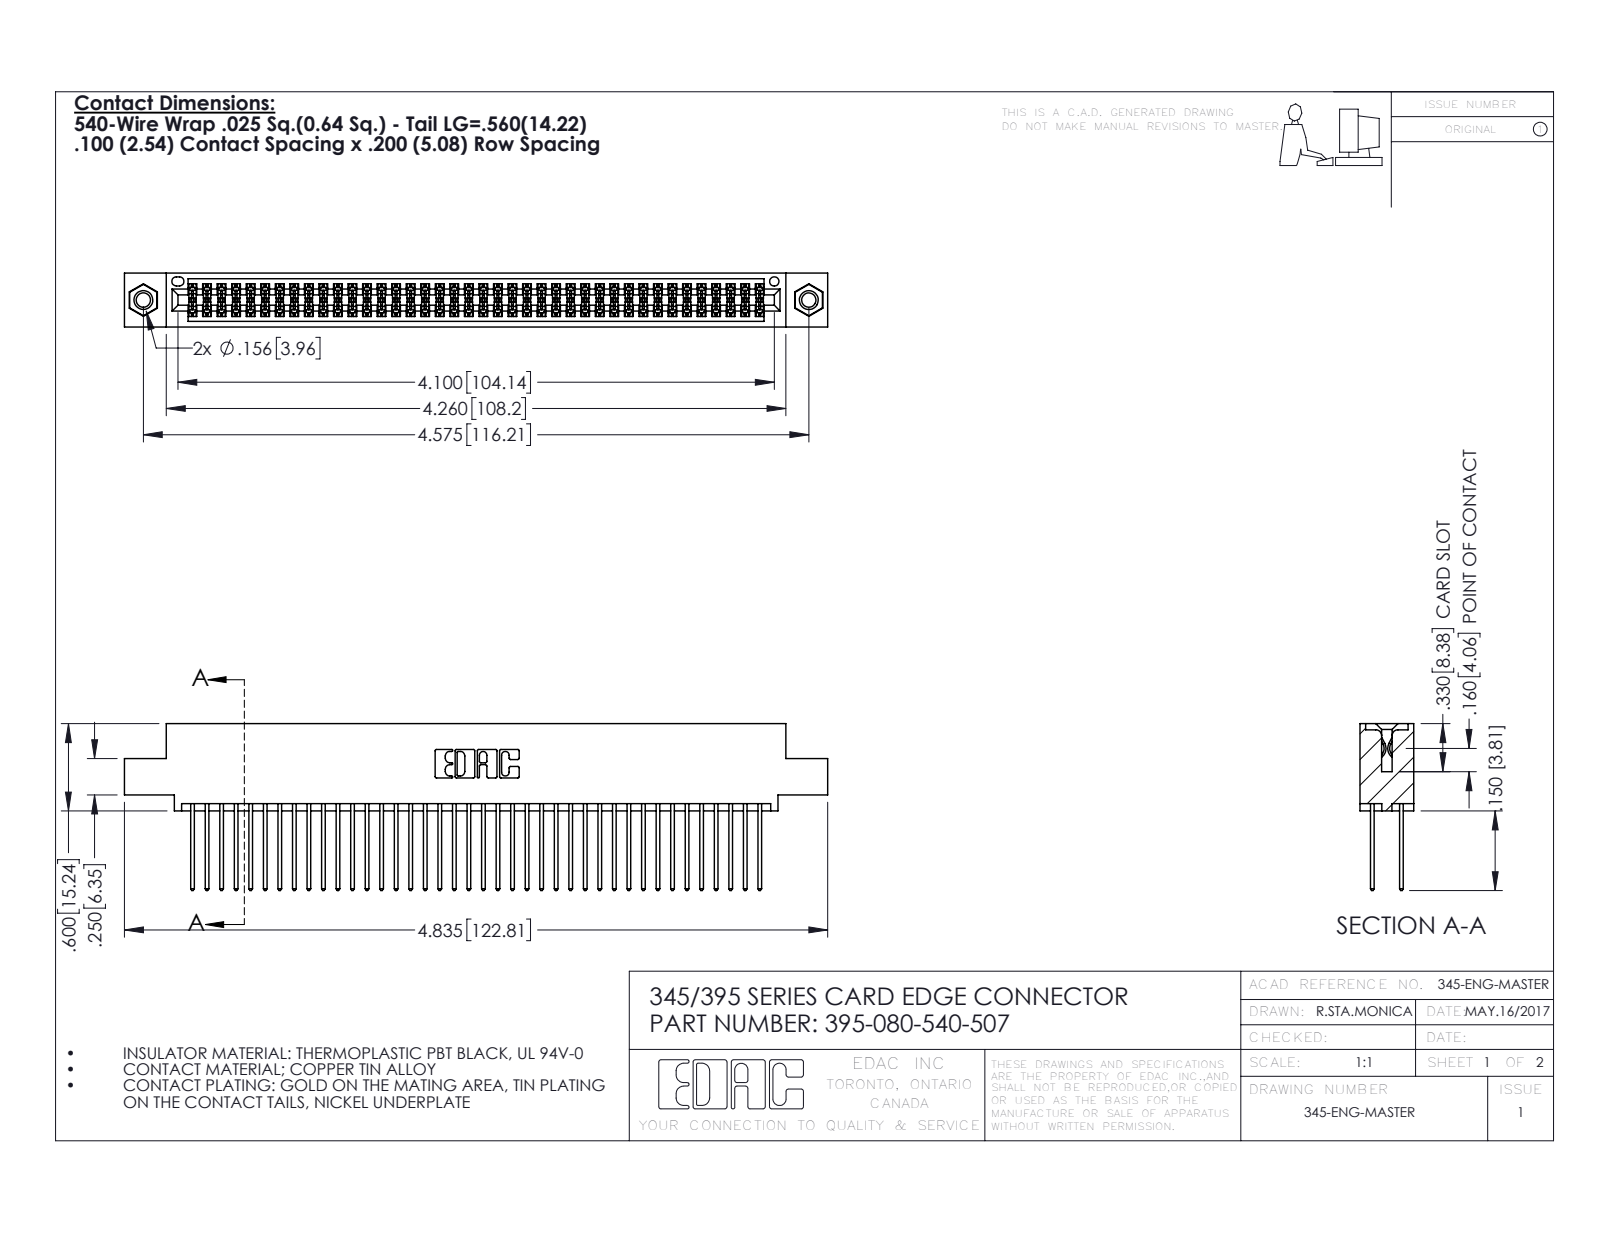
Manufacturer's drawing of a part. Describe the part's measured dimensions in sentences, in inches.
The part is named "345-292-001_345-293-140; 345 Part_0.110 Offset - 0.156 Dia-TI; 395-080-540-507; 345-250-001_345-250-005-103". Its 3-D file was written by "SolidWorks 2016 (CONFIG_CONTROL_DESIGN)". It is 83 solids with 4190 faces: 2756 planar, 1418 cylindrical and 16 other. Overall it measures 4.835 by 1.147 by 0.37 inches. Its volume is 0.74 cubic inches and its surface area 30.09 square inches. Round holes: 2 of diameter 0.098, 2 of diameter 0.125, 2 of diameter 0.156, 1 of diameter 0.064. Round bosses or shafts: 2 of diameter 0.155. Partial cylindrical surfaces (rounded edges, fillets, slot ends): 120 of radius 0.006, 80 of radius 0.01, 22 of radius 0.01, 6 of radius 0.007, 6 of radius 0.031, 3 of radius 0.026, 2 of radius 0.014, 2 of radius 0.019. The main face-to-face distances are 0.072, 0.298, 0.2, 0.098, 0.272, 0.025, 0.37, 0.225, 0.175, 0.149. The hole center spacings are 0.27, 4.339, 4.575.
